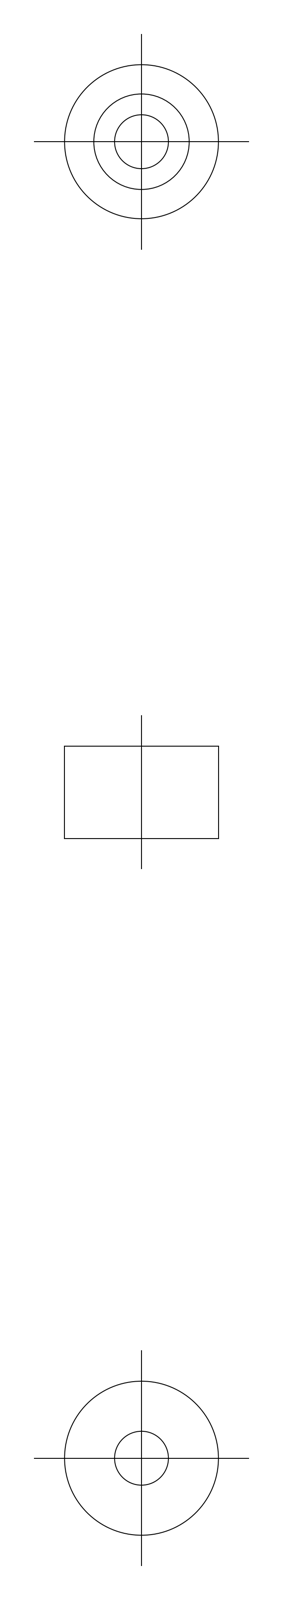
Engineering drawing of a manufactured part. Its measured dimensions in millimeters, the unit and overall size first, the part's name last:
Units: millimetres
Overall size (bounding box): 10 × 10 × 6
Volume: 402 mm³ · Surface area: 386 mm²
Bodies: 1 solid, 8 faces (0 planar, 0 cylindrical, 8 other)
Part name (STEP PRODUCT): stopper
STEP written by: CADfix (AUTOMOTIVE_DESIGN)
